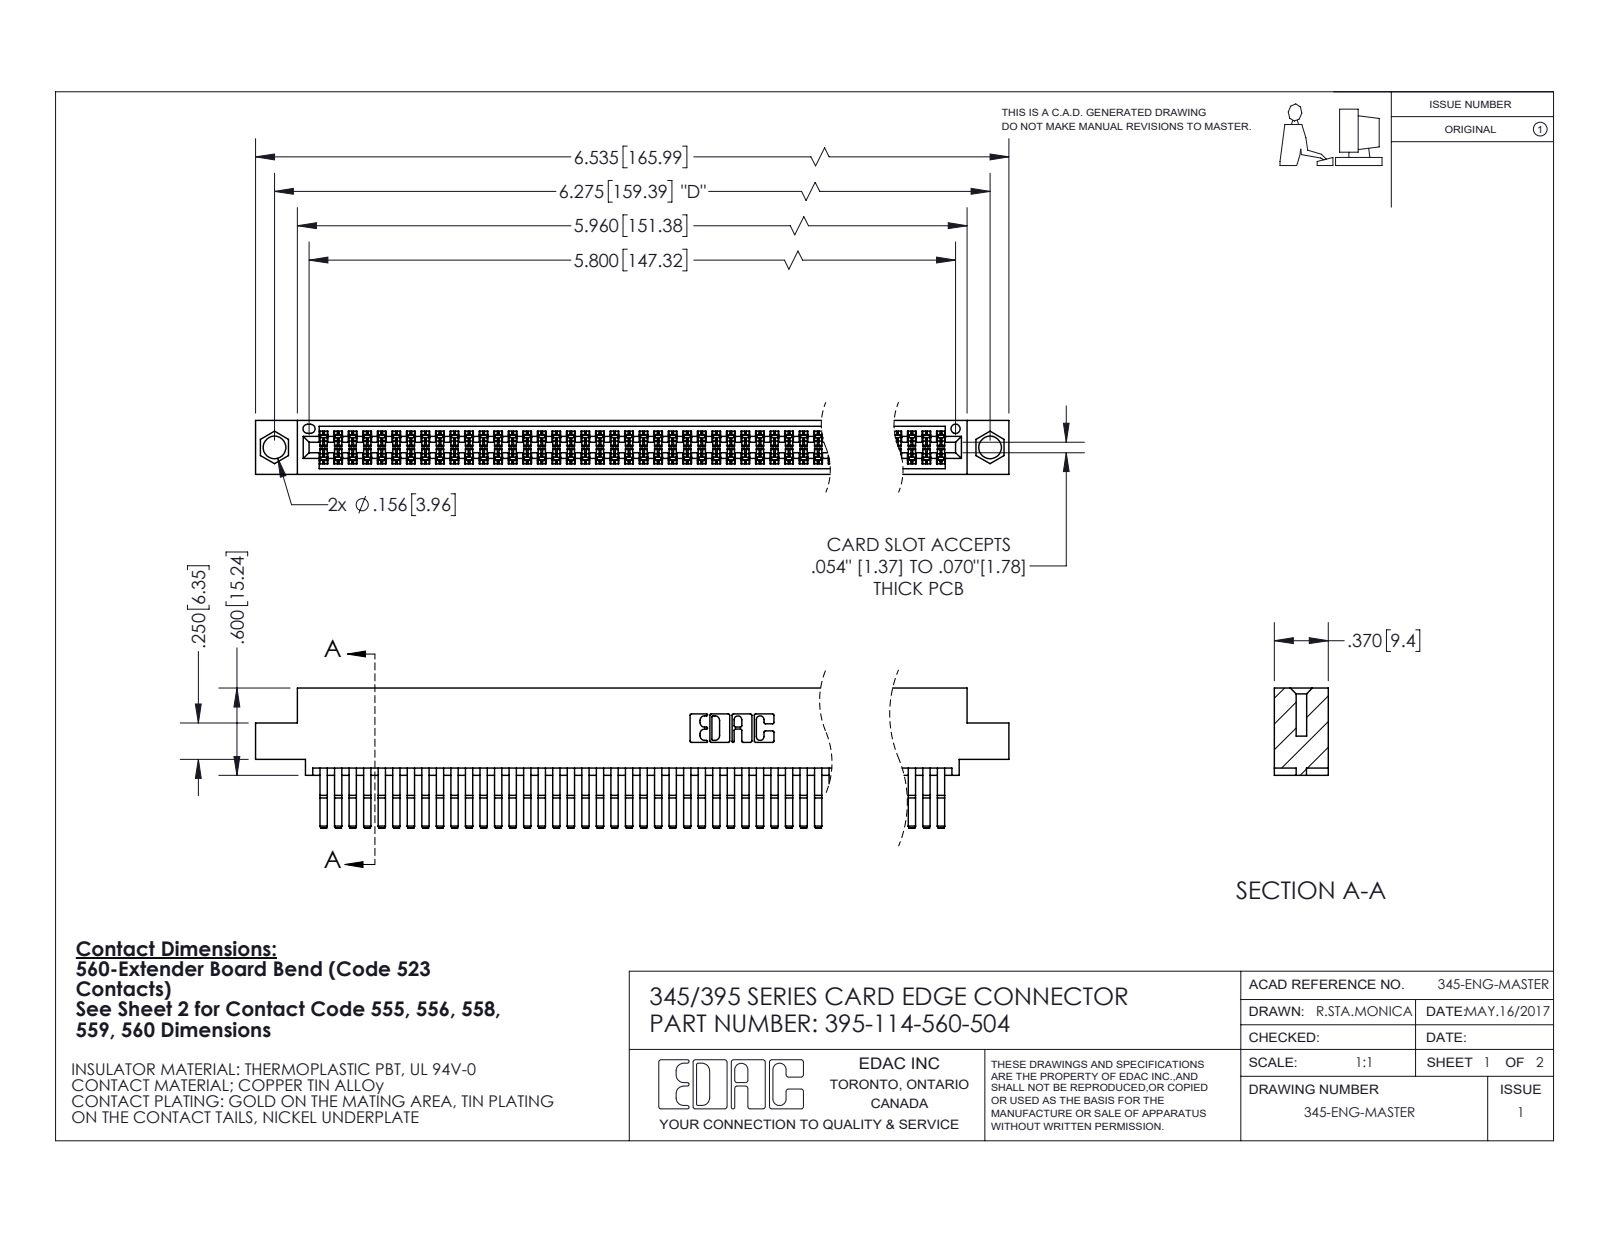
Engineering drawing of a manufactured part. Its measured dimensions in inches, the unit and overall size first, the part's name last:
Units: inches
Overall size (bounding box): 6.535 × 0.962 × 0.37
Round holes (diameter × count): ⌀0.156 ×2, ⌀0.064 ×1
Partial cylindrical surfaces — rounded edges, fillets, slot ends (radius × count): R0.006 ×172, R0.01 ×22, R0.007 ×6, R0.031 ×6, R0.026 ×3, R0.01 ×2, R0.014 ×2, R0.019 ×2
Main face-to-face distances: 0.025, 0.298, 0.072, 0.37, 0.2, 0.098, 0.272, 0.225, 0.175, 0.149
Hole centre spacings: 0.27, 6.039, 6.275
Volume: 1.027 in³ · Surface area: 41.91 in²
Bodies: 115 solids, 6072 faces (3860 planar, 2212 cylindrical, 0 other)
Part name (STEP PRODUCT): 395-114-560-504; 345 Part_0.110 Offset - 0.156 Dia-TI; 345-292-001_560 Tail
STEP written by: SolidWorks 2020 (CONFIG_CONTROL_DESIGN)
